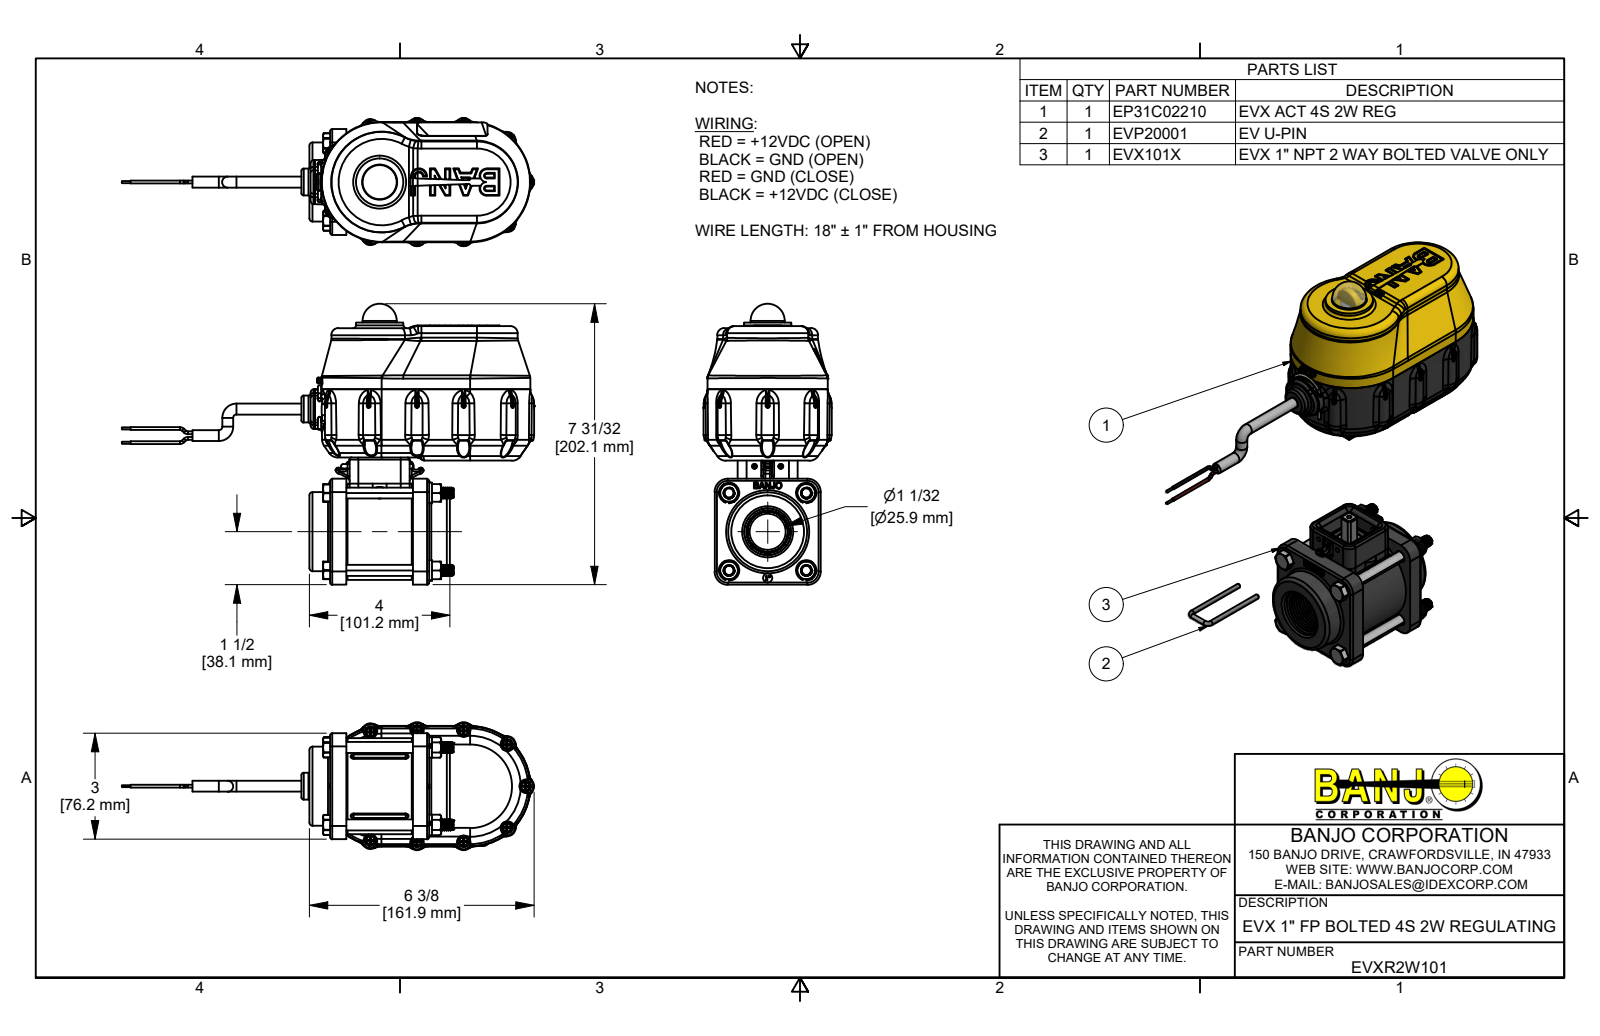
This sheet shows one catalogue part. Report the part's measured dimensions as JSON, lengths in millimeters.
{"part_name": "EVXR2W101; EVP20001; EVX101X; MEVX10254A (+8 more)", "step_written_by": "Autodesk Inventor 2019 (AUTOMOTIVE_DESIGN)", "units": "millimeters", "bodies": {"solids": 95, "faces": 12827, "planar": 3638, "cylindrical": 3441, "other": 5748}, "overall_size": [984.8, 202.1, 92.2], "volume_mm3": 822600, "surface_area_mm2": 477700, "round_holes": [[3.8, 13], [2.4, 11], [2.7, 4], [3.2, 4], [3.4, 4], [3.5, 4], [4.3, 4], [6.4, 4], [8.2, 4], [8.9, 4], [25.9, 3], [2.3, 2]], "round_bosses_or_shafts": [[6.8, 60], [6.4, 17], [3.6, 11], [2.7, 11], [2.2, 11], [2, 10], [8, 5], [14.8, 4]], "partial_cylinders_radius": [[1, 147], [0.5, 83], [1.5, 62], [0.3, 56], [0.1, 41], [0.8, 32], [2, 28], [2.5, 22]], "face_to_face_distances": [2.5, 65.2, 42.8, 62.6, 19.8, 1.4, 11.7, 3.2, 4.2, 22.4], "hole_center_spacings": [55.7, 26.6, 32.6, 39.4, 42.2, 48, 80.9, 83.7]}
